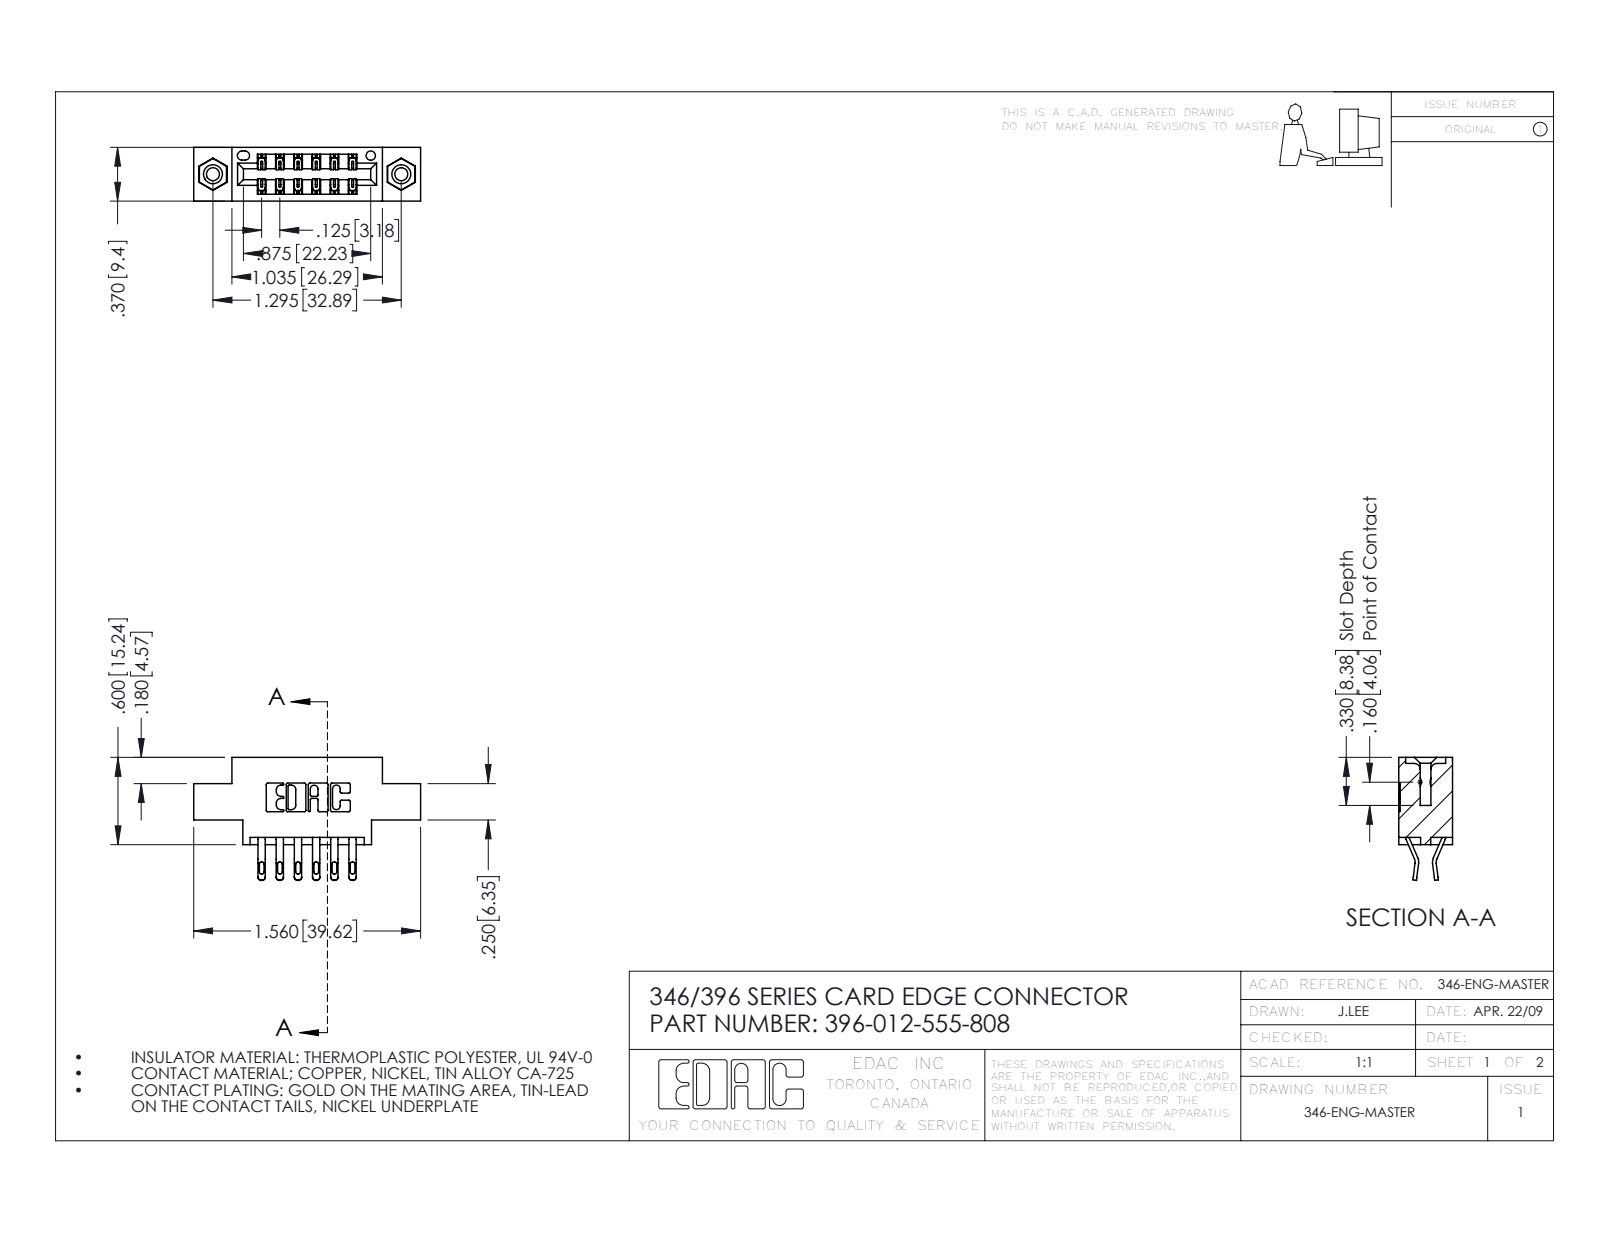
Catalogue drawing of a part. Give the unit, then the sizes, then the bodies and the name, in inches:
Units: inches
Overall size (bounding box): 1.56 × 0.845 × 0.37
Round holes (diameter × count): ⌀0.089 ×2, ⌀0.125 ×2, ⌀0.156 ×2, ⌀0.064 ×1
Round bosses / shafts (diameter × count): ⌀0.155 ×2
Partial cylindrical surfaces — rounded edges, fillets, slot ends (radius × count): R0.016 ×24, R0.02 ×24, R0.01 ×22, R0.006 ×18, R0.007 ×6, R0.031 ×6, R0.026 ×3, R0.01 ×2
Main face-to-face distances: 0.25, 0.37, 0.048, 0.322, 0.222, 0.148, 0.1, 0.174, 0.025, 0.072
Hole centre spacings: 0.246, 1.092, 1.295
Volume: 0.211 in³ · Surface area: 6.992 in²
Bodies: 15 solids, 882 faces (508 planar, 358 cylindrical, 16 other)
Part name (STEP PRODUCT): 396-012-555-808; 345-250-001_345-250-003-102; 345-292-001_555 Tail; 346 Part_0.170 Offset - 0.156 Dia-TI
STEP written by: SolidWorks 2016 (CONFIG_CONTROL_DESIGN)
